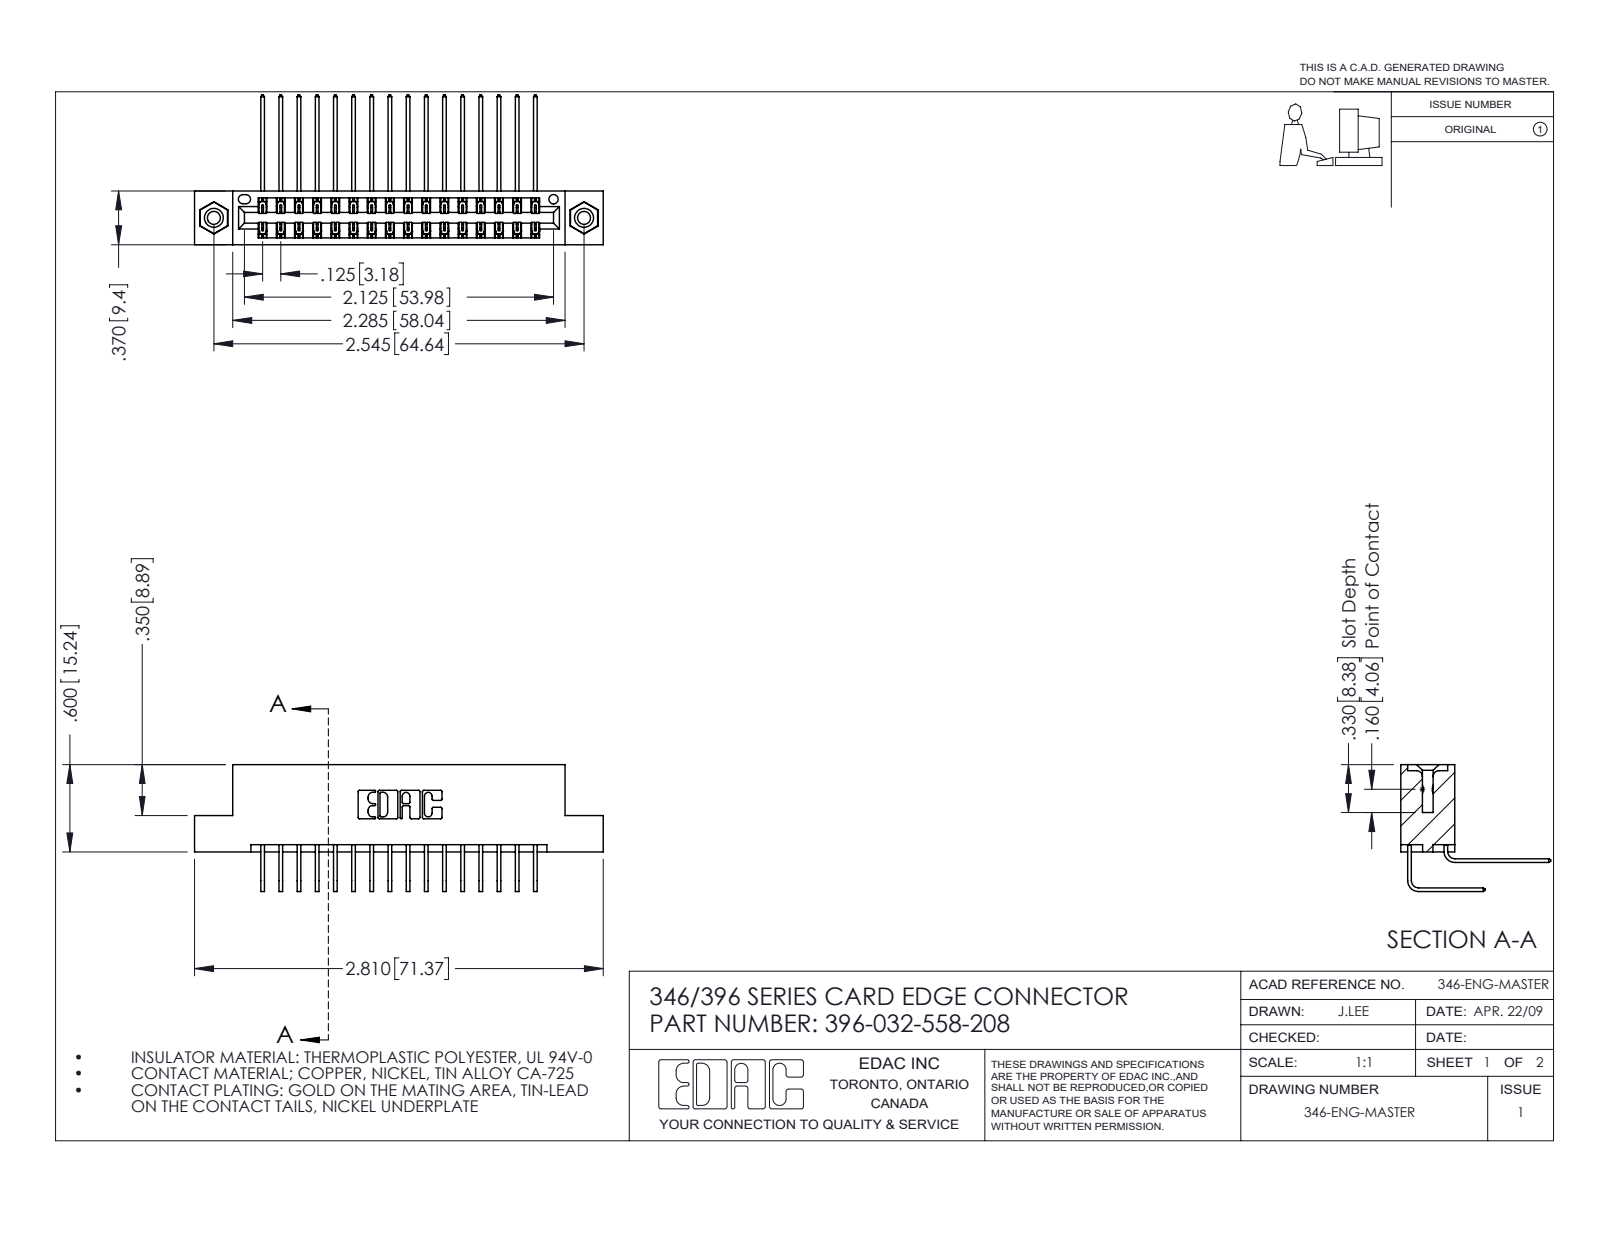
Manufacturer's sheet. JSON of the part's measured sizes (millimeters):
{"part_name": "345-292-001_558 Tail - 2; 396-032-558-208; 346 Part_Flush Mounting Lugs - 0.156 Dia-TI; 345-250-001_345-250-003-102 (+1 more)", "step_written_by": "SolidWorks 2016 (CONFIG_CONTROL_DESIGN)", "units": "millimeters", "bodies": {"solids": 35, "faces": 1910, "planar": 1292, "cylindrical": 602, "other": 16}, "overall_size": [71.4, 26.2, 22.2], "volume_mm3": 6930, "surface_area_mm2": 10030, "round_holes": [[2.3, 2], [3.2, 2], [4, 2], [1.6, 1]], "round_bosses_or_shafts": [[3.9, 2]], "partial_cylinders_radius": [[0.2, 48], [0.3, 22], [0.2, 6], [0.8, 6], [0.7, 3], [0.4, 2], [0.6, 2], [0.6, 2]], "face_to_face_distances": [8.2, 1.2, 6.4, 0.6, 9.4, 7.6, 1.8, 7, 3.8, 5.6], "hole_center_spacings": [6.2, 59.4, 64.6]}
